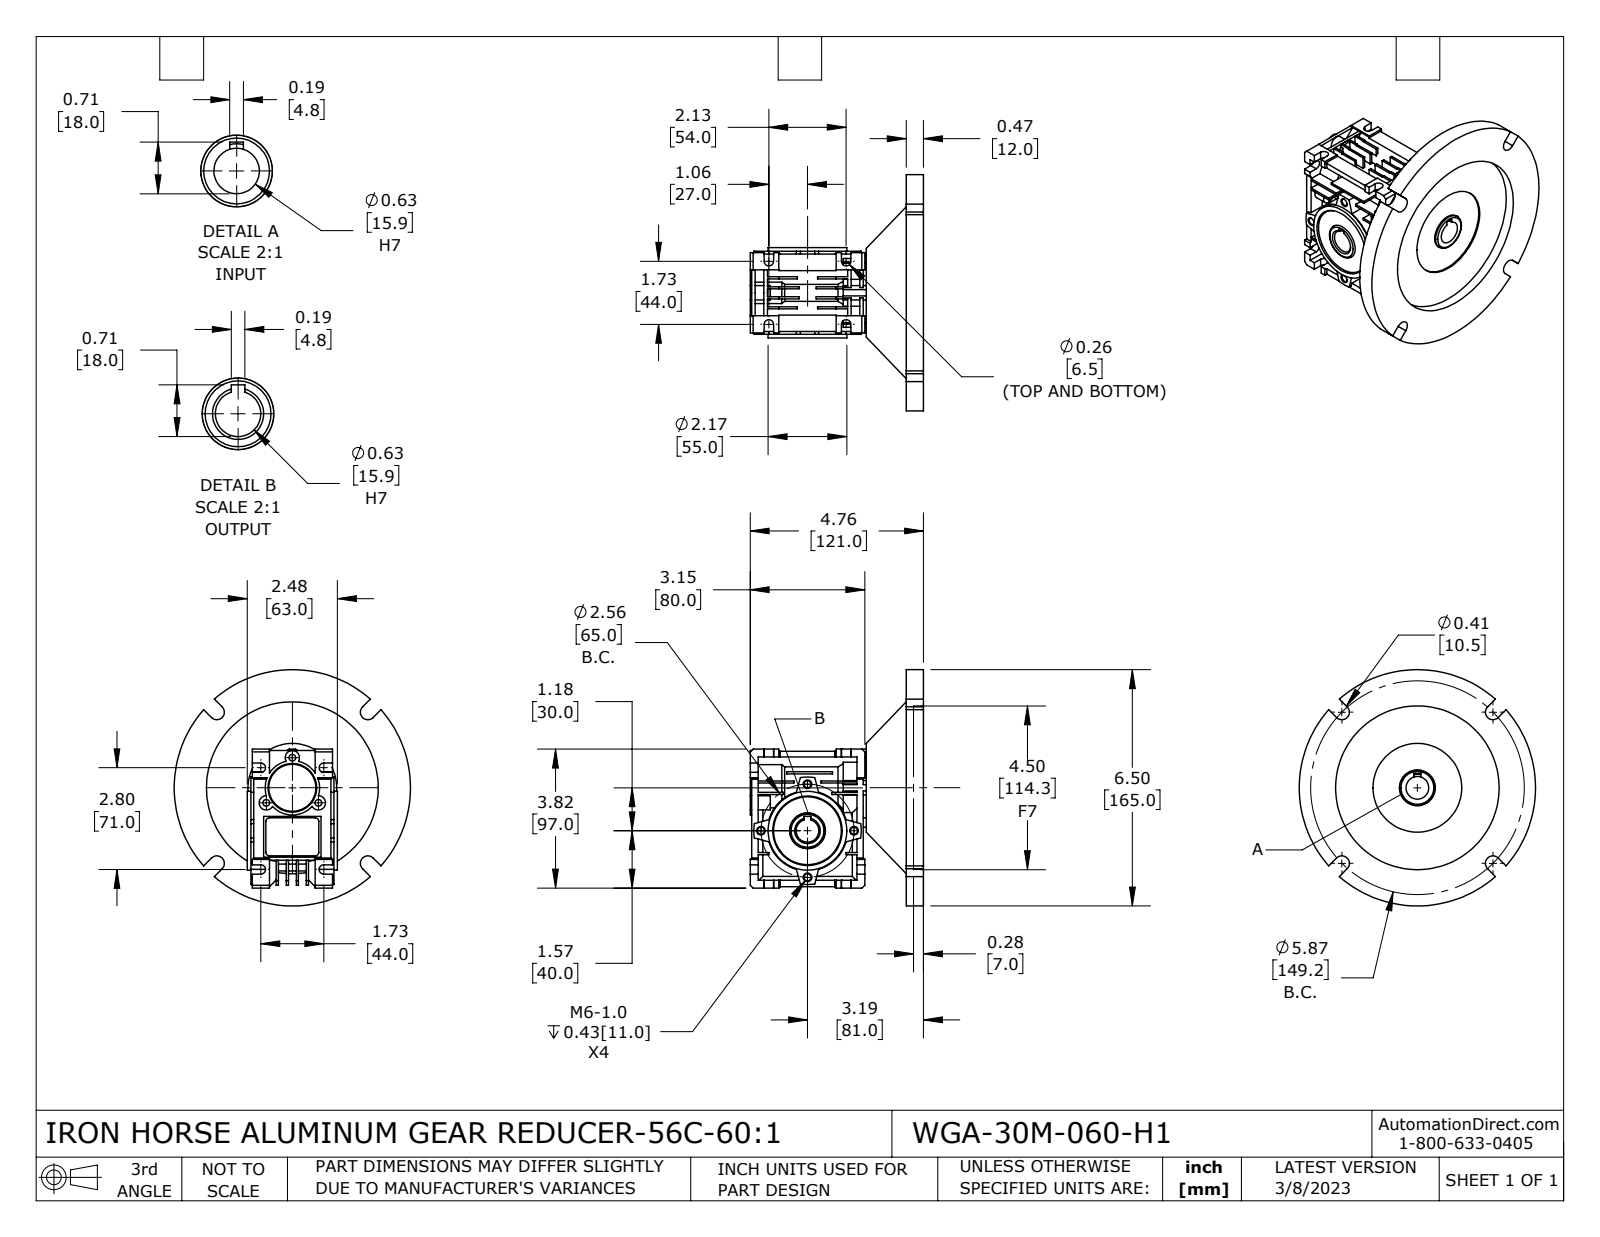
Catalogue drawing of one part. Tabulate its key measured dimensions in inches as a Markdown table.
| quantity | value |
| --- | --- |
| part name | WGA-30M-060-H1 |
| STEP written by | SolidWorks 2021 (CONFIG_CONTROL_DESIGN) |
| units | inches |
| bodies | 1 solid, 682 faces (442 planar, 168 cylindrical, 72 other) |
| overall size | 6.496 × 6.496 × 4.764 |
| volume | 39.8 in³ |
| surface area | 198.1 in² |
| round holes (diameter × count) | 0.194 × 4, 0.194 × 4, 0.183 × 3, 0.625 × 2, 2.441 × 1, 4.5 × 1 |
| round bosses / shafts (diameter × count) | 6.496 × 1, 2.205 × 1, 2.165 × 1, 1.496 × 1, 0.984 × 1 |
| partial cylindrical surfaces (radius × count) | 0.128 × 8, 0.197 × 7, 0.098 × 4, 0.207 × 4, 0.374 × 1, 0.669 × 1, 0.846 × 1, 1.476 × 1 |
| main face-to-face distances | 0.276, 0.059, 0.039, 0.472, 0.217, 0.197, 0.177, 0.551, 0.335, 0.157 |
| hole center spacings | 1.28, 1.809, 0.827, 1.432, 2.559, 1.432 |
